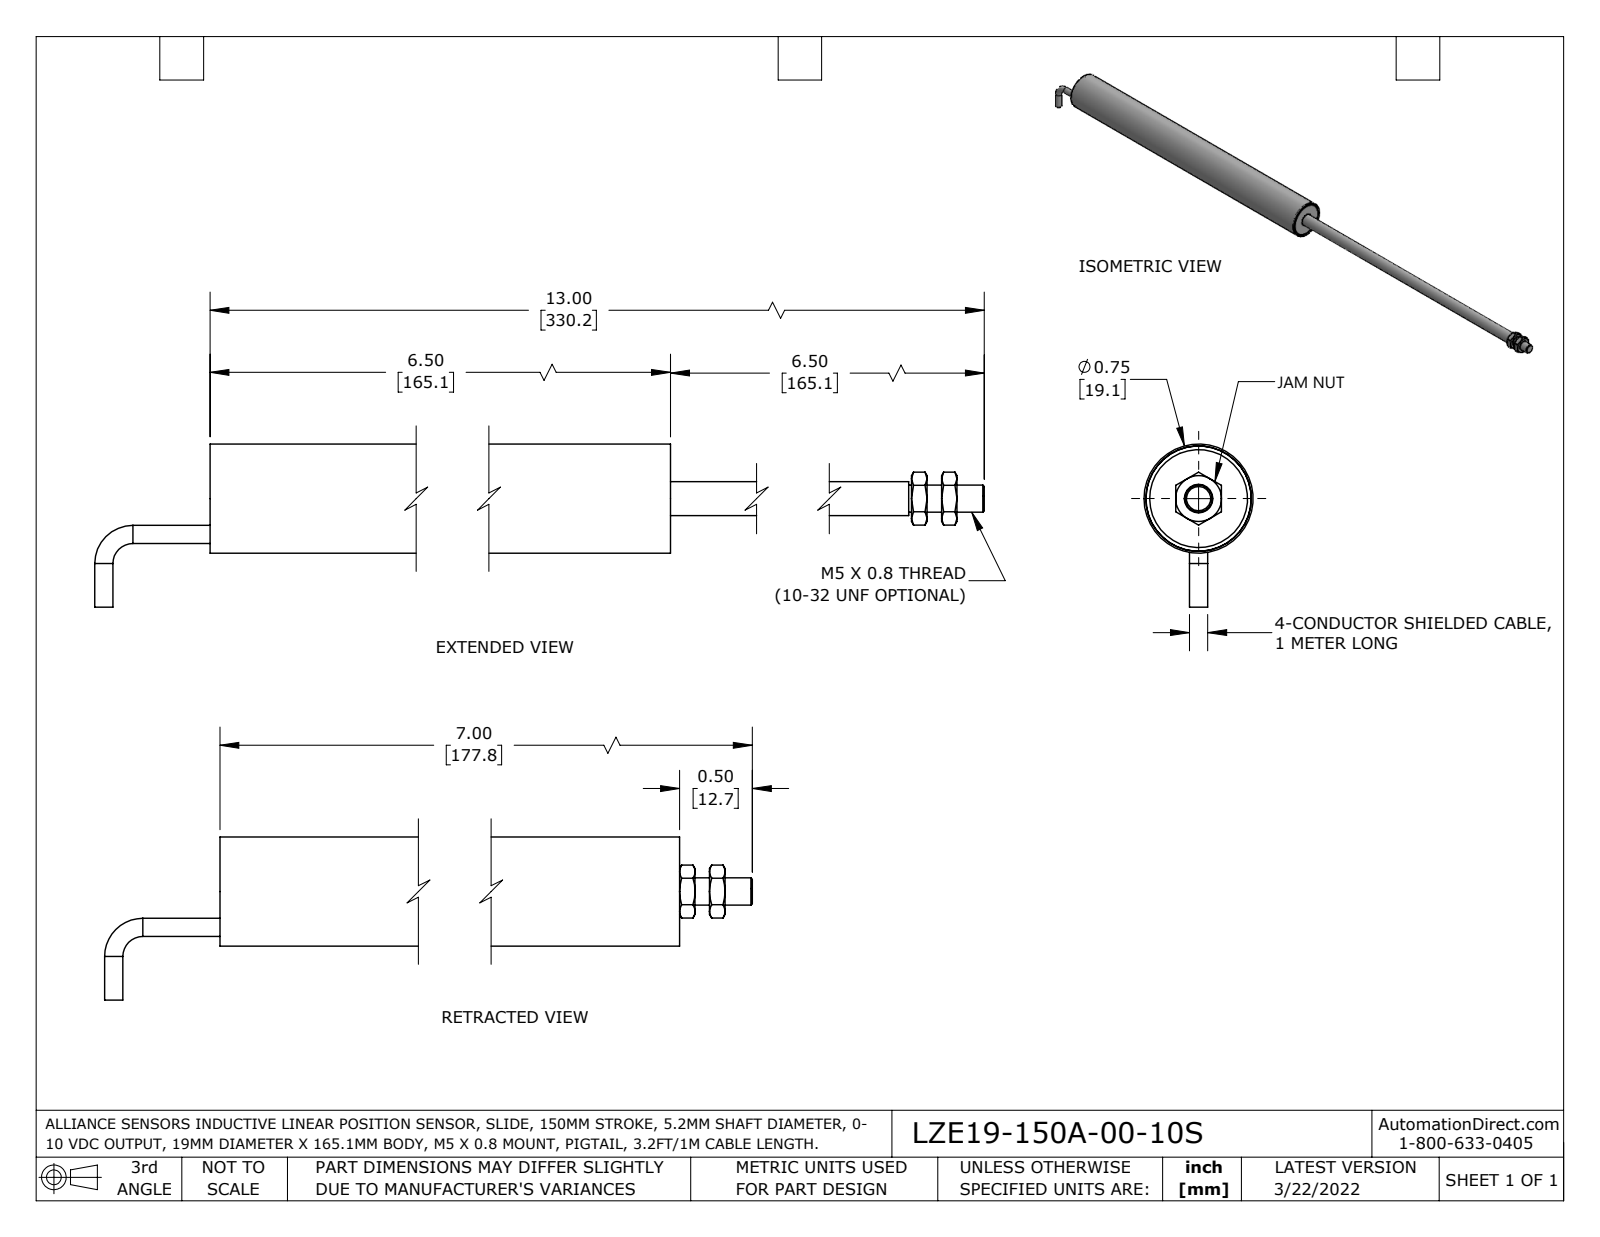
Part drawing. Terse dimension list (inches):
name: 3120-0009-06_-06; 3120-0007-ZY_with slot; 3120-0007-ZY; LZE19-150A-00-10S (+6 more)
written by: SolidWorks 2021 (AUTOMOTIVE_DESIGN)
unit: in
bodies: 10 solids, 137 faces (42 planar, 44 cylindrical, 51 other)
size: 13.793 × 1.121 × 0.75
volume: 1.012 in³; area: 56.49 in²
holes: 1× ⌀0.165, 1× ⌀0.188, 1× ⌀0.197, 1× ⌀0.234, 1× ⌀0.281, 1× ⌀0.68, 1× ⌀0.725
bosses: 2× ⌀0.125, 1× ⌀0.75, 1× ⌀0.723, 1× ⌀0.278, 1× ⌀0.187
rounds: 1× R0.052
face distances: 0.06, 6.42, 0.08, 6.36, 6.48, 0.315, 0.206, 0.106, 0.374, 6.5
